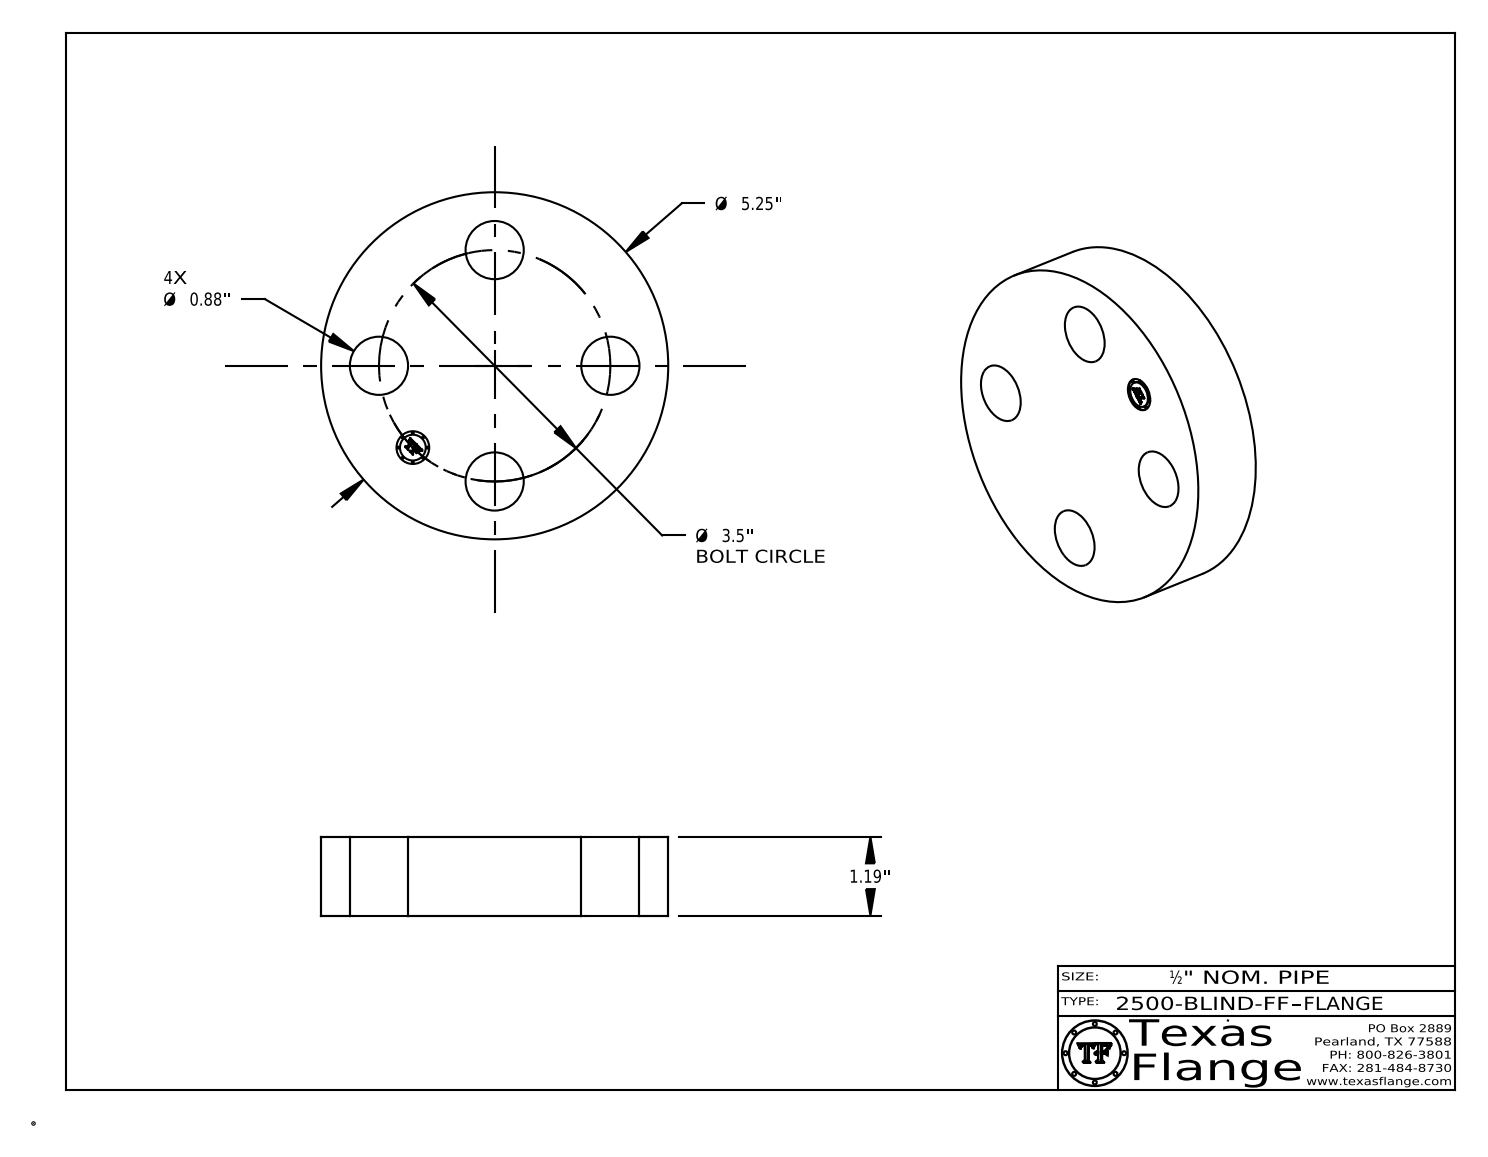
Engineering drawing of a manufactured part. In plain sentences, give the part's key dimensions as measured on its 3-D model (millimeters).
The part is named "2500-BLIND-FF". Its 3-D file was written by "CATIA V5 STEP AP214 (AUTOMOTIVE_DESIGN)". It is 1 solid with 397 faces: 367 planar, 30 cylindrical and 0 other. Overall it measures 133.4 by 133.4 by 30.2 millimeters. Its volume is 374 600 cubic millimeters and its surface area 46 010 square millimeters. Round holes: 4 of diameter 22.4, 1 of diameter 12.6. Round bosses or shafts: 8 of diameter 0.8, 1 of diameter 133.4, 1 of diameter 9.9. The main face-to-face distances are 30.2, 29.8, 0.4, 3.8, 3.7, 0.7, 2.4, 3.1, 0.5, 1.9. The hole center spacings are 62.9, 34, 82.1, 88.9.
